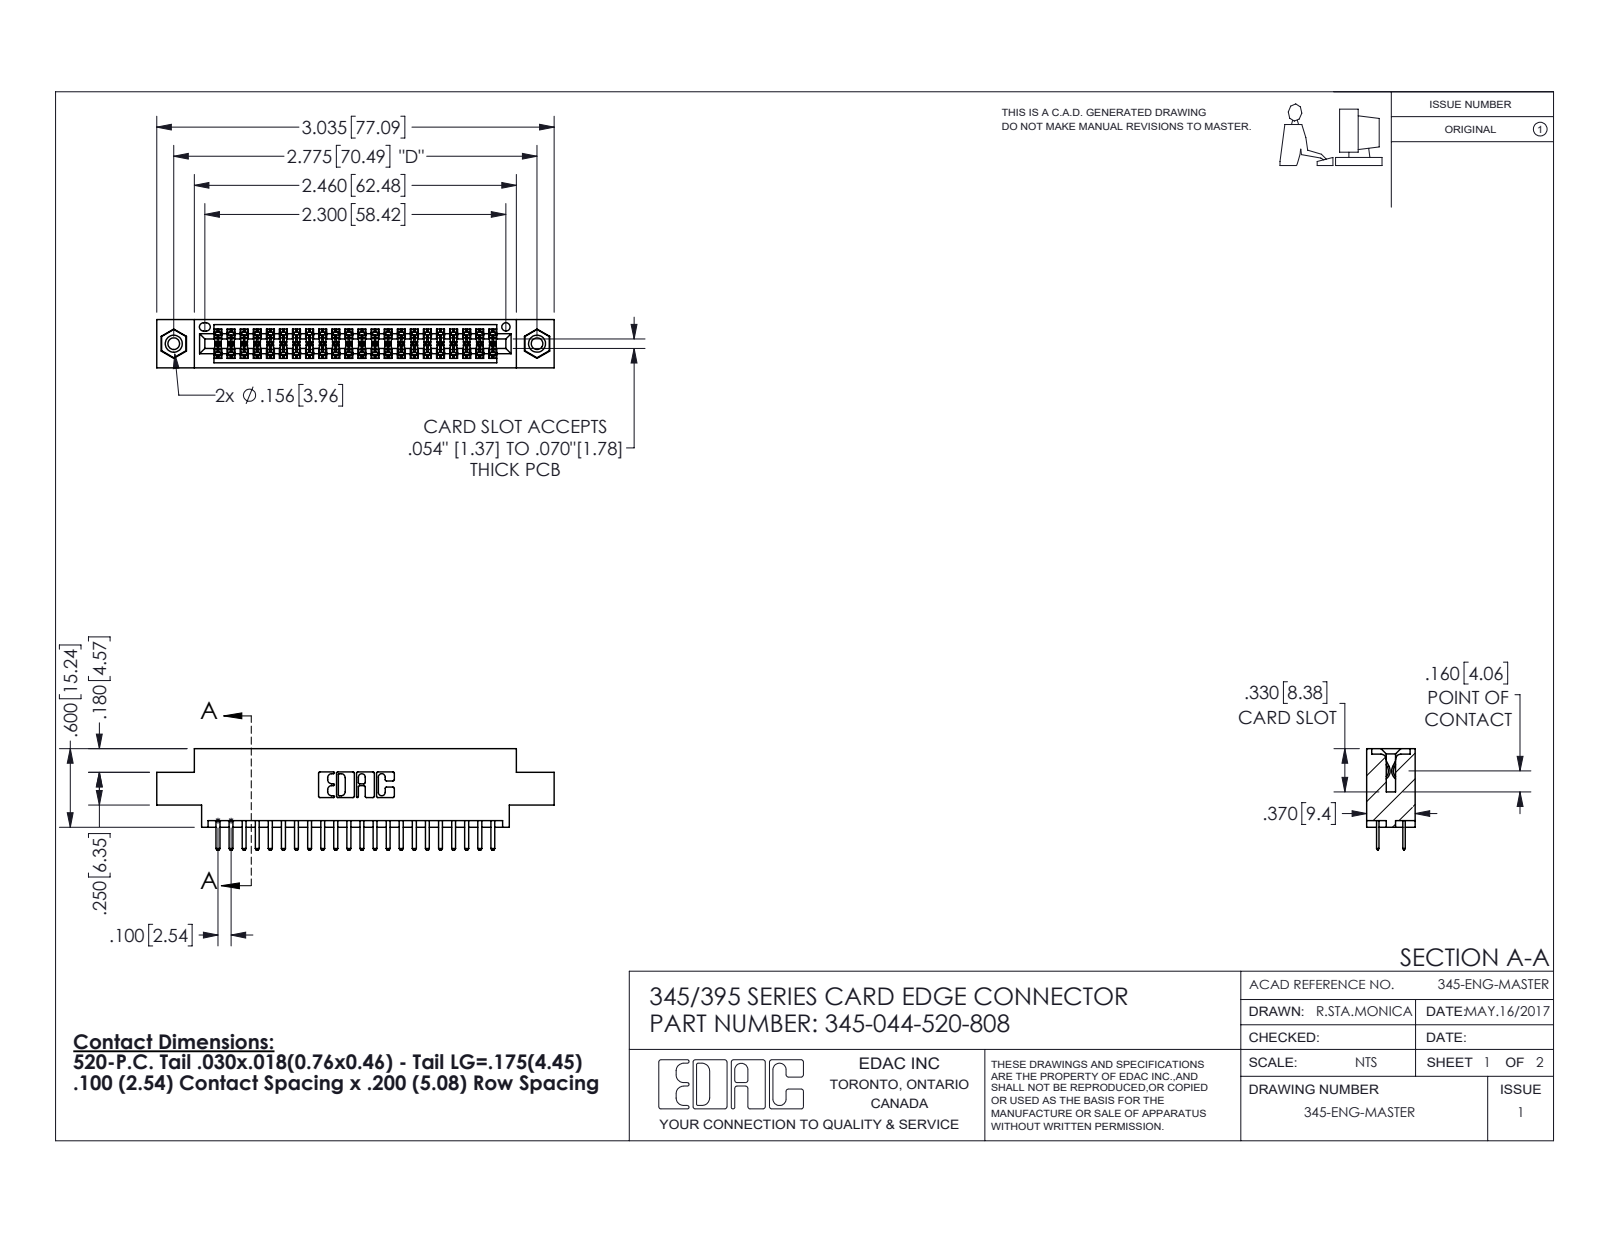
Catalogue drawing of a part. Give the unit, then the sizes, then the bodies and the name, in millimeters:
Units: millimetres
Overall size (bounding box): 77.1 × 19.7 × 9.4
Round holes (diameter × count): ⌀2.3 ×2, ⌀3.2 ×2, ⌀4 ×2, ⌀1.6 ×1
Round bosses / shafts (diameter × count): ⌀3.9 ×2
Partial cylindrical surfaces — rounded edges, fillets, slot ends (radius × count): R0.2 ×66, R0.3 ×48, R0.3 ×22, R0.2 ×6, R0.8 ×6, R0.7 ×3, R0.4 ×2, R0.5 ×2
Main face-to-face distances: 1.8, 7.6, 5.1, 9.4, 2.5, 6.9, 0.6, 5.7, 0.6, 4.4
Hole centre spacings: 6.9, 64.5, 70.5
Volume: 7 160 mm³ · Surface area: 10 320 mm²
Bodies: 47 solids, 2566 faces (1656 planar, 894 cylindrical, 16 other)
Part name (STEP PRODUCT): 345-292-001_345-293-120; 345 Part_0.170 Offset - 0.156 Dia-TI; 345-044-520-808; 345-250-001_345-250-003-102
STEP written by: SolidWorks 2016 (CONFIG_CONTROL_DESIGN)
